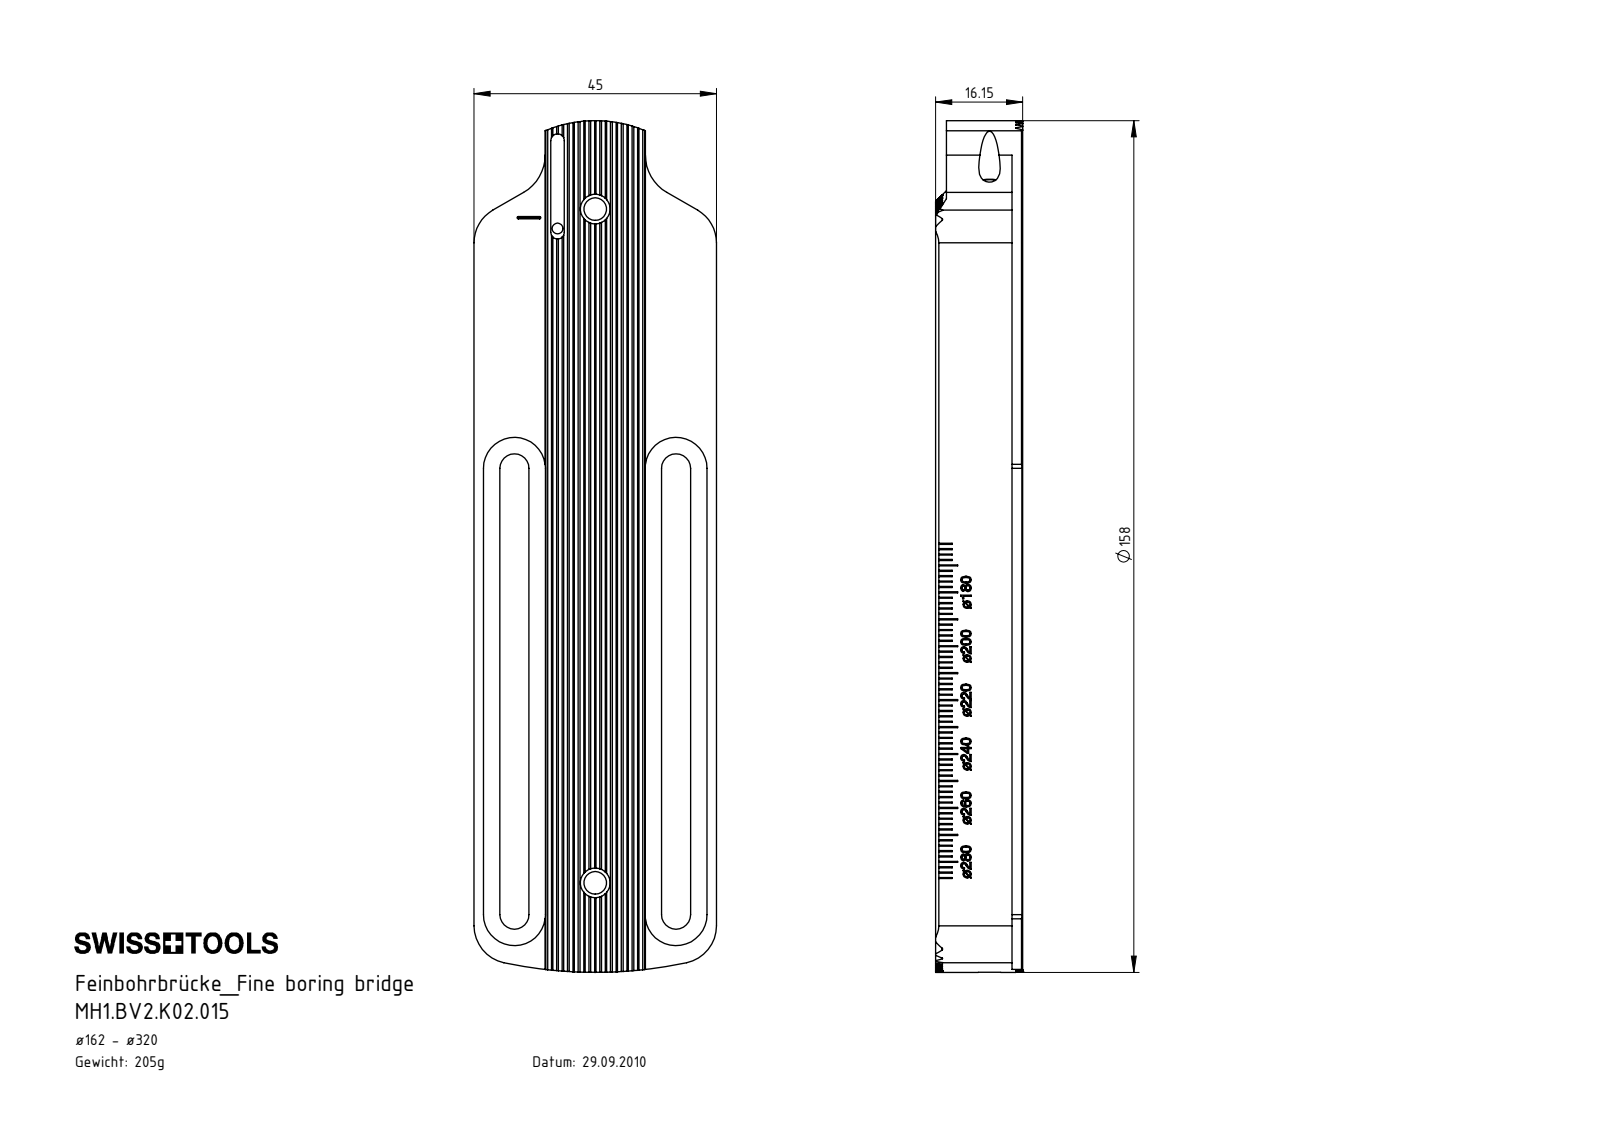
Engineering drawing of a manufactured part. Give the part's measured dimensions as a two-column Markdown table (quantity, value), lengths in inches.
| quantity | value |
| --- | --- |
| part name | MH1-BV2.K02.015_B; MH1.BV2.K02.015; BN 1392 - M5 x 16; ISO 4026 - M4 x 5 (+1 more) |
| STEP written by | SolidWorks 2017 (AUTOMOTIVE_DESIGN) |
| units | inches |
| bodies | 8 solids, 1068 faces (708 planar, 98 cylindrical, 262 other) |
| overall size | 6.22 × 1.772 × 1.054 |
| volume | 4.456 in³ |
| surface area | 49.08 in² |
| round holes (diameter × count) | 0.165 × 6, 0.13 × 5, 0.217 × 2, 0.079 × 1, 0.118 × 1 |
| round bosses / shafts (diameter × count) | 0.157 × 5, 0.433 × 1, 0.335 × 1, 0.197 × 1 |
| partial cylindrical surfaces (radius × count) | 0.006 × 31, 0.106 × 4, 0.226 × 4, 0.276 × 4, 0.049 × 2, 0.315 × 2, 0.945 × 1, 3.189 × 1 |
| main face-to-face distances | 0.068, 0.136, 0.341, 0.273, 0.636, 0.205, 0.227, 1.181, 0.12, 0.333 |
| hole center spacings | 0.787, 0.31, 0.843, 1.575, 1.63, 2.378, 2.417, 2.504 |
